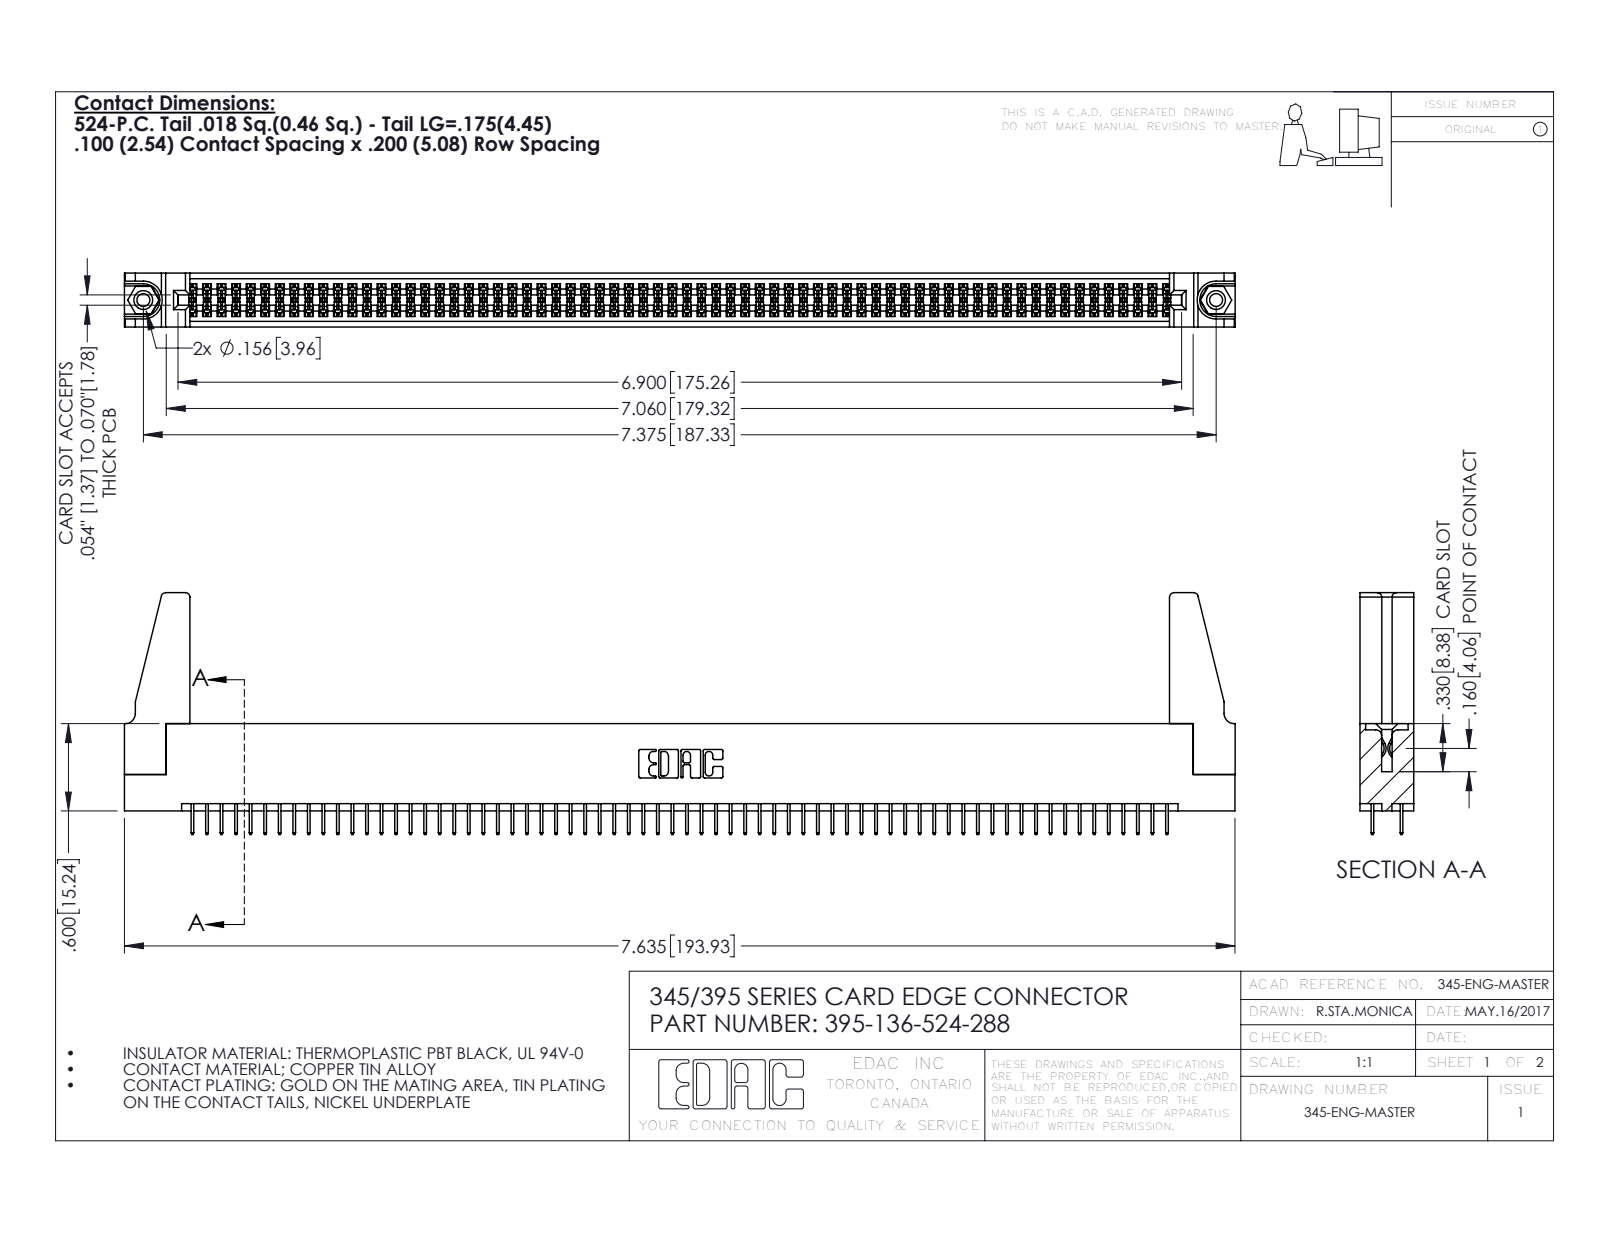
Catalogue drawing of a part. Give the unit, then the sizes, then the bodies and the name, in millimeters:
Units: millimetres
Overall size (bounding box): 194 × 42.2 × 9.4
Round holes (diameter × count): ⌀2.3 ×2, ⌀3.2 ×2, ⌀4 ×2, ⌀1.6 ×1
Round bosses / shafts (diameter × count): ⌀3.9 ×2
Partial cylindrical surfaces — rounded edges, fillets, slot ends (radius × count): R0.2 ×204, R0.3 ×22, R0.8 ×8, R0.2 ×6, R0.8 ×6, R0.7 ×3, R0.4 ×2, R0.5 ×2
Main face-to-face distances: 1.8, 7.6, 9.4, 5.1, 2.5, 6.9, 0.6, 5.7, 1.8, 4.4
Hole centre spacings: 6.9, 181.3, 187.3
Volume: 22 120 mm³ · Surface area: 30 990 mm²
Bodies: 141 solids, 7594 faces (5456 planar, 2122 cylindrical, 16 other)
Part name (STEP PRODUCT): 395-136-524-288; 345-220-078_345-220-088; 345 Part_Flush Mounting Lugs - 0.156 Dia-TH; 345-250-001_345-250-001-102 (+1 more)
STEP written by: SolidWorks 2016 (CONFIG_CONTROL_DESIGN)
